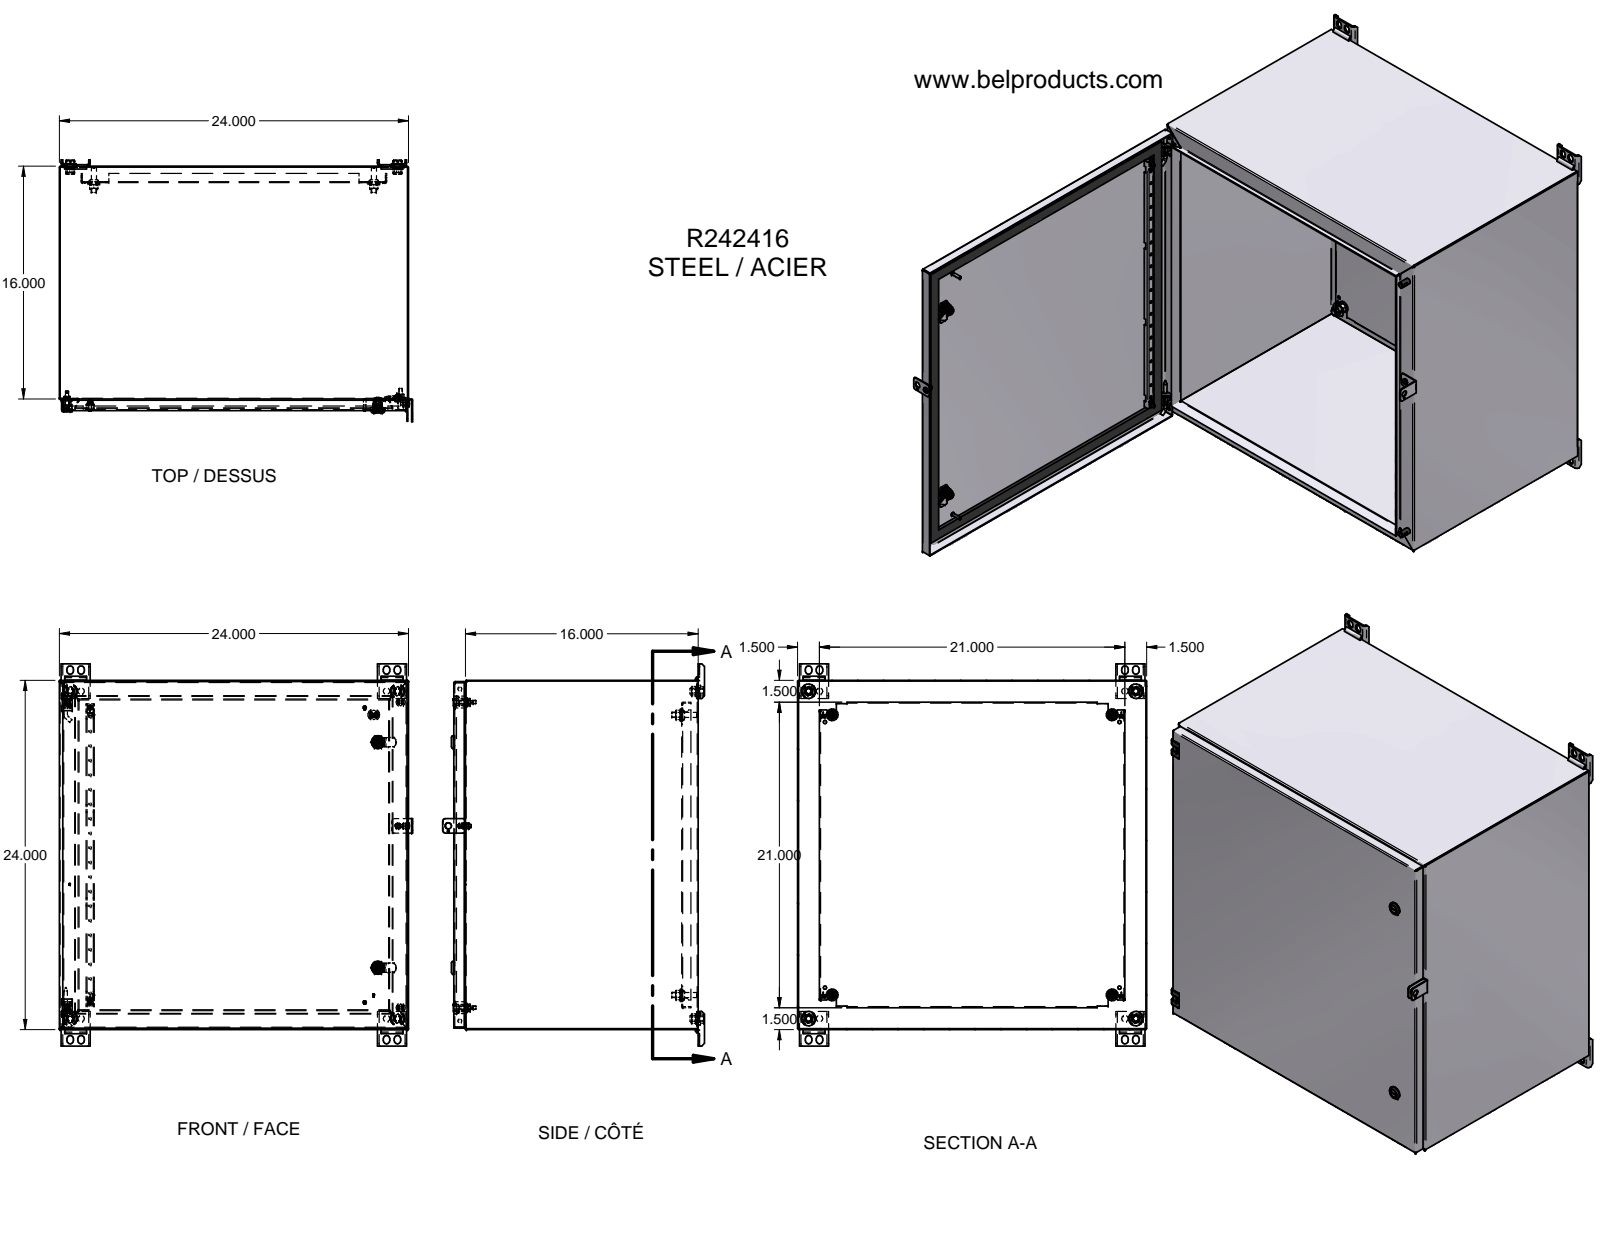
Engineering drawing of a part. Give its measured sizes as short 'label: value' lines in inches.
name: 0.375 DIA; CAOUTCHOUC; METAL; LOCK AVEC TOURNEVIS TYPE 4-12 SANS CAME (+8 more)
written by: Unknown (AUTOMOTIVE_DESIGN)
unit: in
bodies: 94 solids, 3610 faces (2072 planar, 640 cylindrical, 898 other)
size: 26.266 × 24.282 × 17.995
volume: 233.8 in³; area: 7 146 in²
holes: 20× ⌀0.184, 10× ⌀0.125, 8× ⌀0.375, 8× ⌀0.406, 8× ⌀0.456, 6× ⌀0.014, 4× ⌀0.159, 4× ⌀0.236, 4× ⌀0.265, 4× ⌀0.281, 4× ⌀0.355, 4× ⌀0.415
bosses: 10× ⌀0.119, 8× ⌀0.812, 5× ⌀0.19, 4× ⌀0.637, 4× ⌀0.353, 4× ⌀0.256, 4× ⌀0.031, 4× ⌀0.02
rounds: 84× R0.008, 26× R0.032, 22× R0.375, 18× R0.012, 16× R0.01, 16× R0.092, 16× R0.228, 12× R0.187
face distances: 0.06, 23.94, 16.731, 23.88, 24, 16.672, 16.791, 0.075, 15.735, 15.676
hole spacings: 20.938, 22.5, 0.515, 0.625, 0.75, 0.781, 1.225, 1.5
